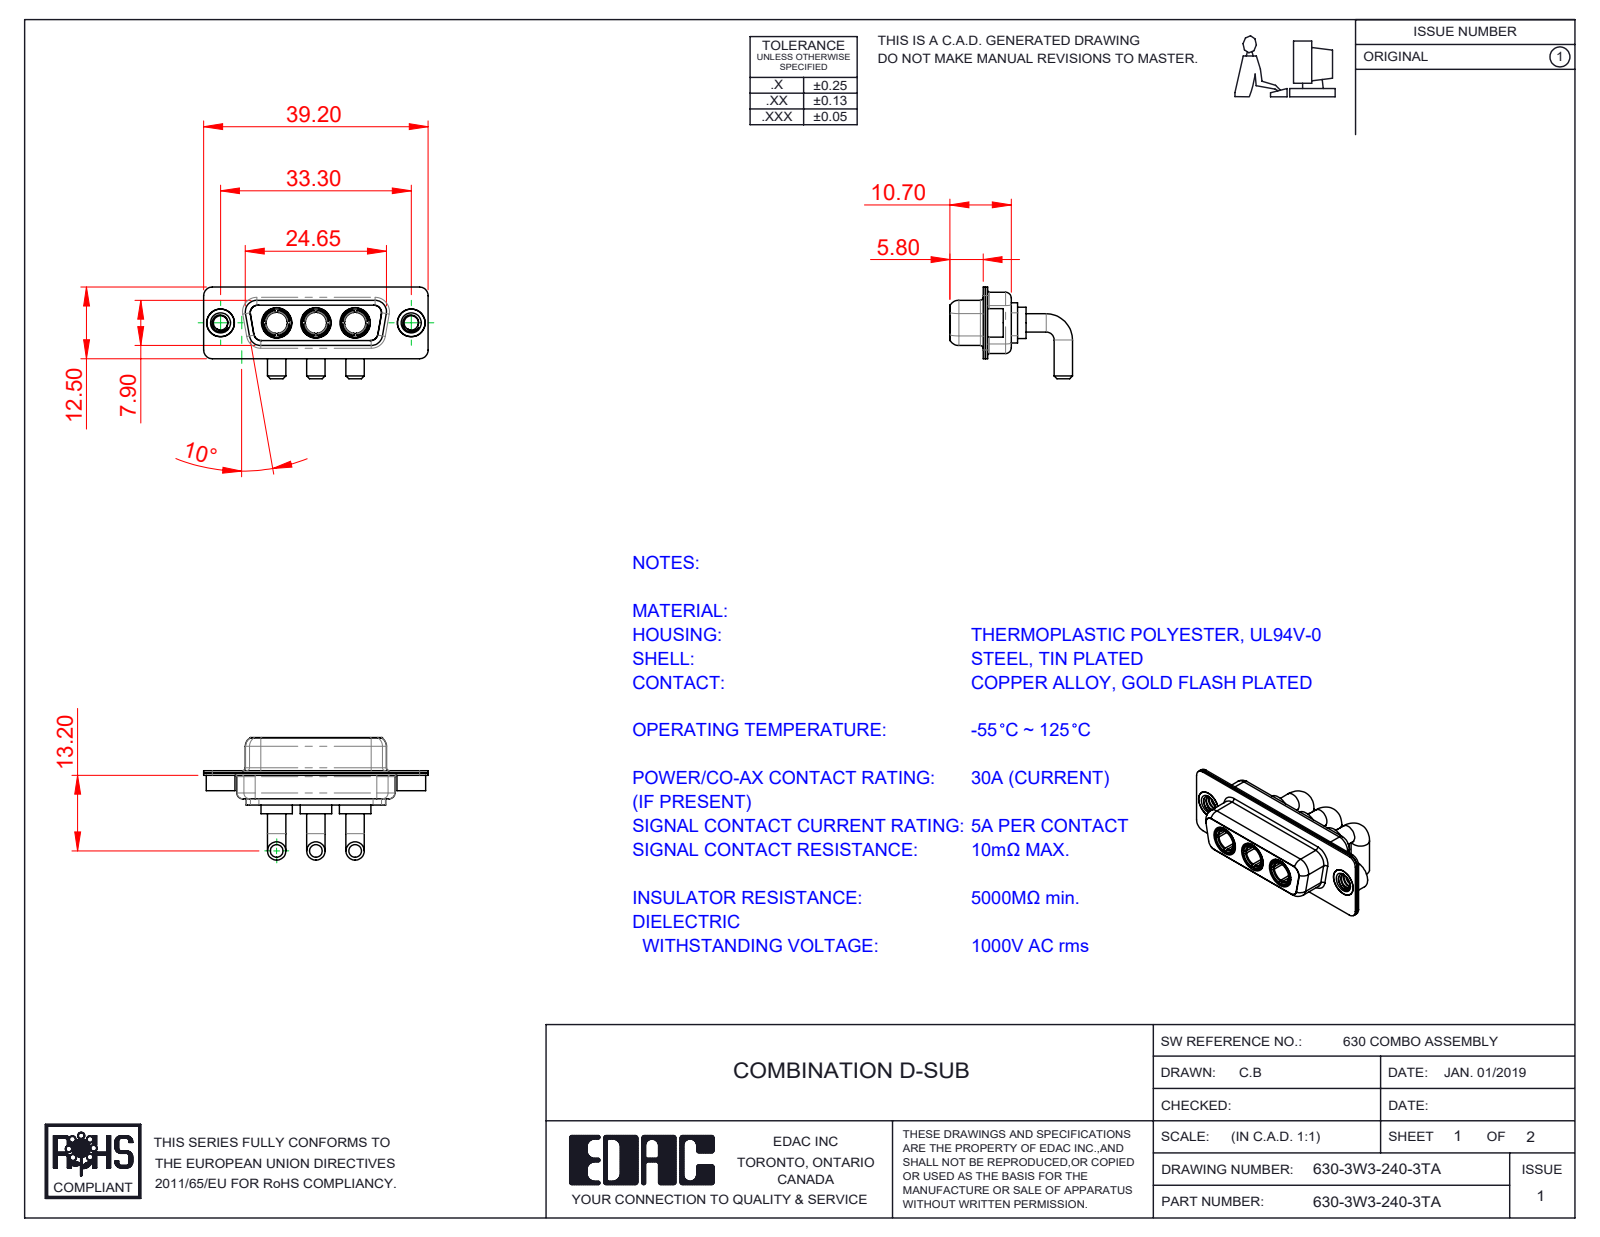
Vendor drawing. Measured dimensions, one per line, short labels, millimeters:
name: 630Combo Shell Front_15 Contacts; 630Combo Housing_3W3; Power Socket_30A RA; 630Combo Threaded Rivet_A (+2 more)
written by: SolidWorks 2020 (CONFIG_CONTROL_DESIGN)
unit: mm
bodies: 11 solids, 507 faces (154 planar, 210 cylindrical, 143 other)
size: 39.2 × 21.4 × 16
volume: 2 720 mm³; area: 5 983 mm²
holes: 5× ⌀4.85, 3× ⌀3.7, 3× ⌀5.3, 2× ⌀2.5, 2× ⌀4, 2× ⌀4.05
bosses: 6× ⌀3.2, 3× ⌀5.5, 3× ⌀5.2, 3× ⌀4.96, 3× ⌀4.75, 3× ⌀3.75, 2× ⌀5, 2× ⌀4.95
rounds: 16× R1.5, 12× R1.35, 12× R2, 8× R1.6, 4× R0.25, 4× R0.5, 4× R0.6, 4× R0.65
face distances: 0.4, 1.4, 0.45, 8.45, 8.9, 1.8, 6.2, 7.05, 0.8, 7.5
hole spacings: 6.85, 9.8, 16.65, 23.5, 13.7, 33.3
